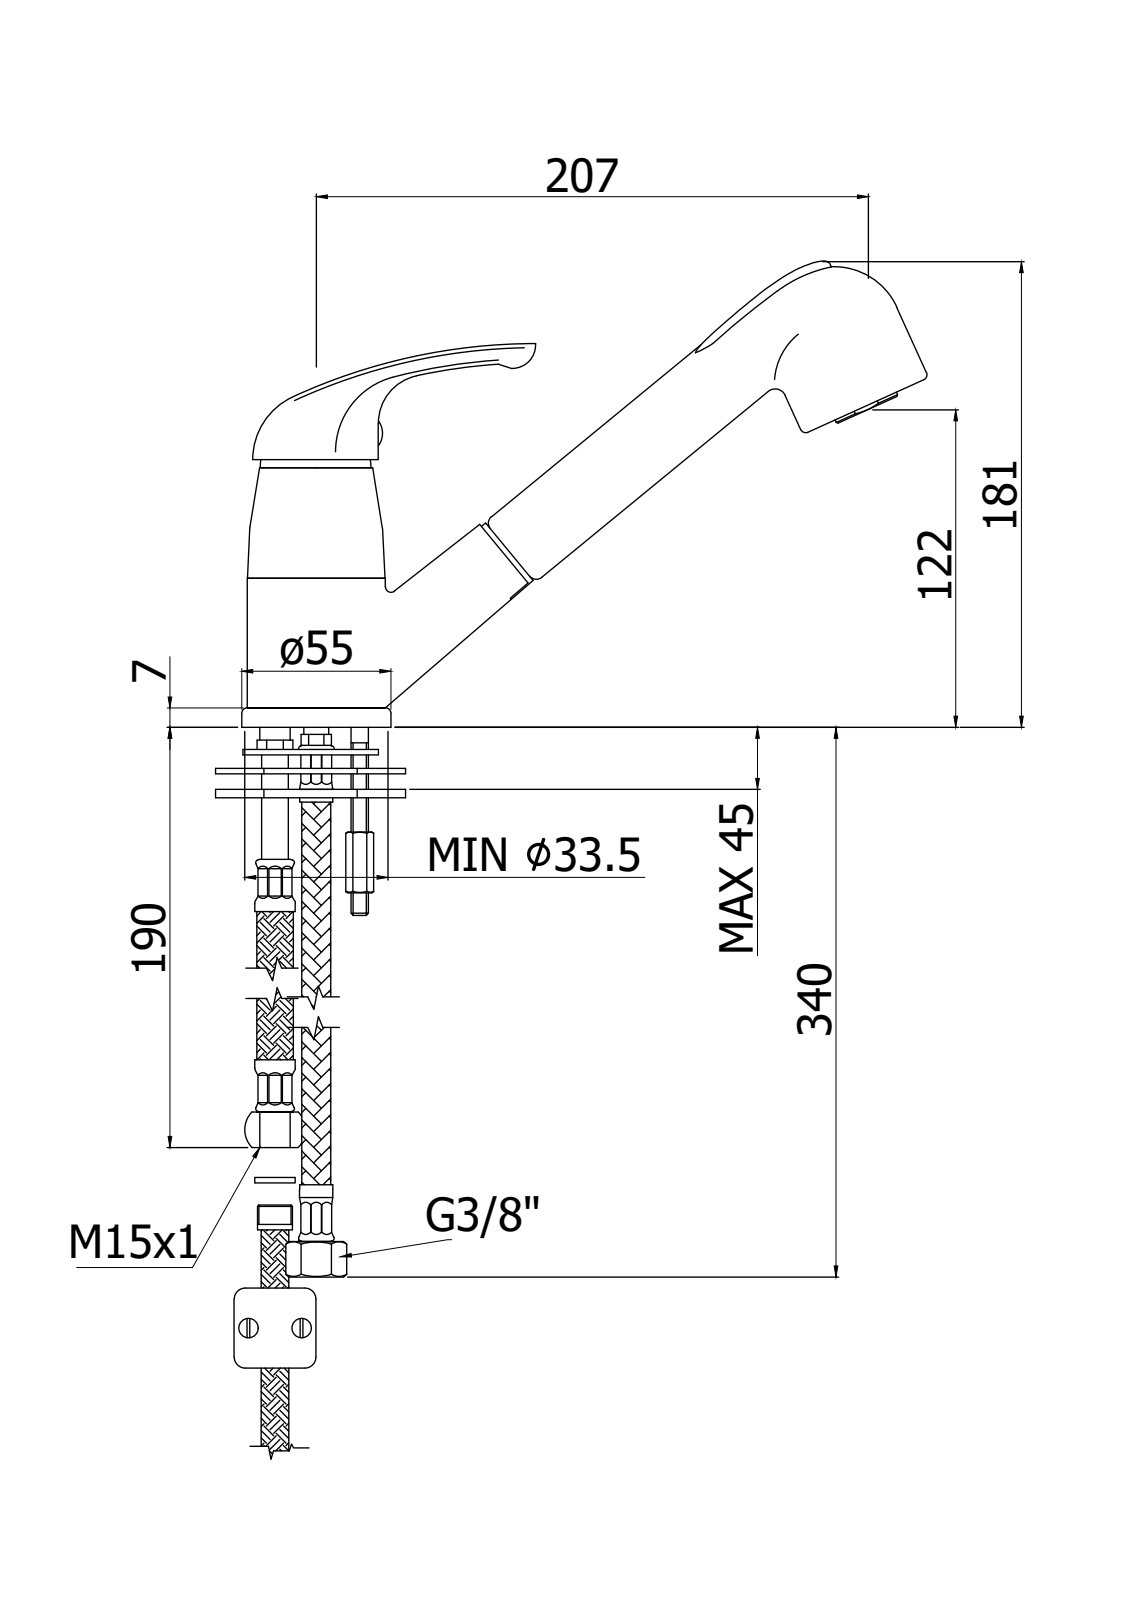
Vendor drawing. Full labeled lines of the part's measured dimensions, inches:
Part name (STEP PRODUCT): APM31183CR
STEP written by: CREO PARAMETRIC BY PTC INC, 2020044 (CONFIG_CONTROL_DESIGN)
Units: inches
Bodies: 1 solid, 1290 faces (697 planar, 324 cylindrical, 269 other)
Overall size (bounding box): 9.927 × 7.135 × 2.205
Volume: 20.95 in³ · Surface area: 191 in²
Round holes (diameter × count): ⌀0.276 ×5, ⌀0.157 ×2, ⌀0.217 ×2, ⌀0.339 ×2, ⌀0.37 ×2, ⌀0.13 ×1, ⌀0.15 ×1, ⌀0.197 ×1, ⌀0.236 ×1, ⌀0.315 ×1, ⌀0.354 ×1, ⌀0.433 ×1
Round bosses / shafts (diameter × count): ⌀0.197 ×2, ⌀2.154 ×1, ⌀1.969 ×1, ⌀1.89 ×1, ⌀1.772 ×1, ⌀1.76 ×1, ⌀1.732 ×1, ⌀1.654 ×1
Partial cylindrical surfaces — rounded edges, fillets, slot ends (radius × count): R0.02 ×24, R0.231 ×16, R0.006 ×11, R0.039 ×10, R0.012 ×4, R0.315 ×3, R0.492 ×2, R0.098 ×1
Main face-to-face distances: 0.02, 0.039, 0.453, 0.433, 0.276, 1.004, 0.118, 3.402, 0.079, 0.189
Hole centre spacings: 0.414, 0.443, 0.449, 0.555, 0.831, 0.969, 0.366, 0.413
